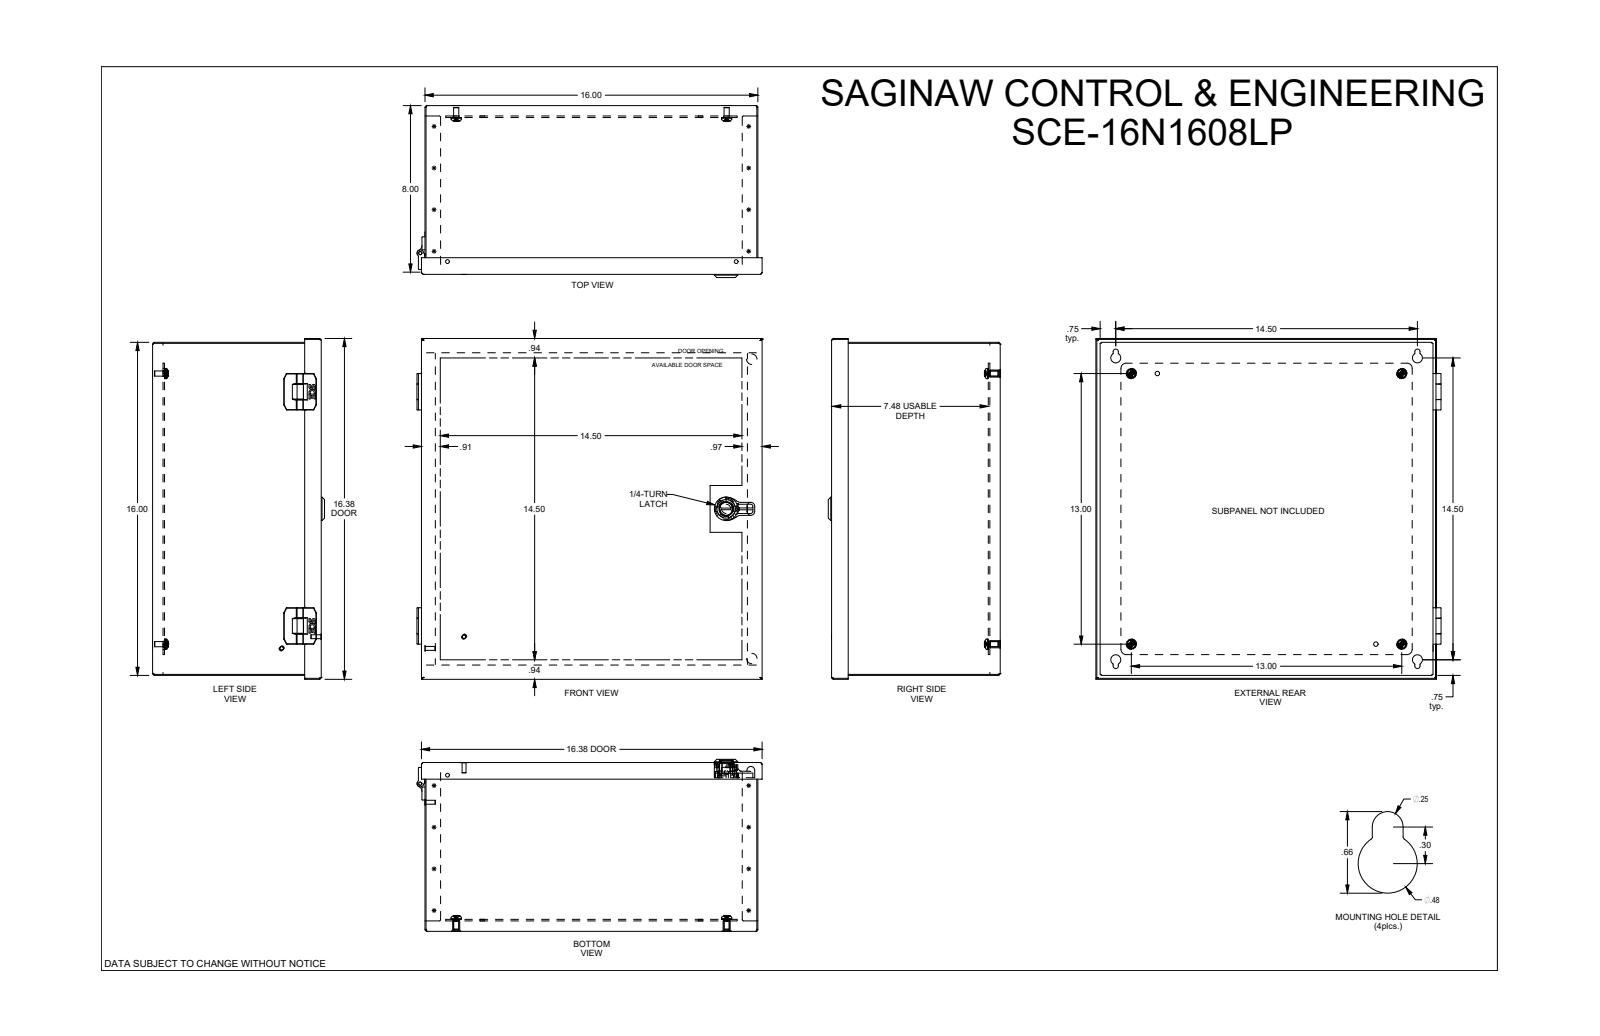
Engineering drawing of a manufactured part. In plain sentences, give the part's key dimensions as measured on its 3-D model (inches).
The part is named "SCE-16N1608LP". Its 3-D file was written by "SolidWorks 2019 (AUTOMOTIVE_DESIGN)". It is 31 solids with 1545 faces: 578 planar, 643 cylindrical and 324 other. Overall it measures 16.593 by 16.375 by 8.267 inches. Its volume is 82.7 cubic inches and its surface area 2 654 square inches. Round holes: 4 of diameter 0.17, 4 of diameter 0.25, 4 of diameter 0.281, 4 of diameter 0.329, 4 of diameter 0.343, 4 of diameter 0.48, 3 of diameter 0.193, 2 of diameter 0.187, 2 of diameter 0.218, 1 of diameter 0.158, 1 of diameter 0.44, 1 of diameter 0.635. Round bosses or shafts: 4 of diameter 0.492, 4 of diameter 0.479, 4 of diameter 0.341, 4 of diameter 0.248, 4 of diameter 0.237, 4 of diameter 0.16, 2 of diameter 0.5, 2 of diameter 0.323. Partial cylindrical surfaces (rounded edges, fillets, slot ends): 253 of radius 0.01, 95 of radius 0.02, 25 of radius 0.06, 24 of radius 0.015, 24 of radius 0.025, 6 of radius 0.055, 6 of radius 0.25, 4 of radius 0.125. The main face-to-face distances are 0.06, 8.047, 15.94, 7.987, 8.107, 16, 15.88, 0.5, 0.44, 0.575. The hole center spacings are 13.77, 1.061, 1.089, 1.091, 11.25, 13, 14.5, 19.445.
